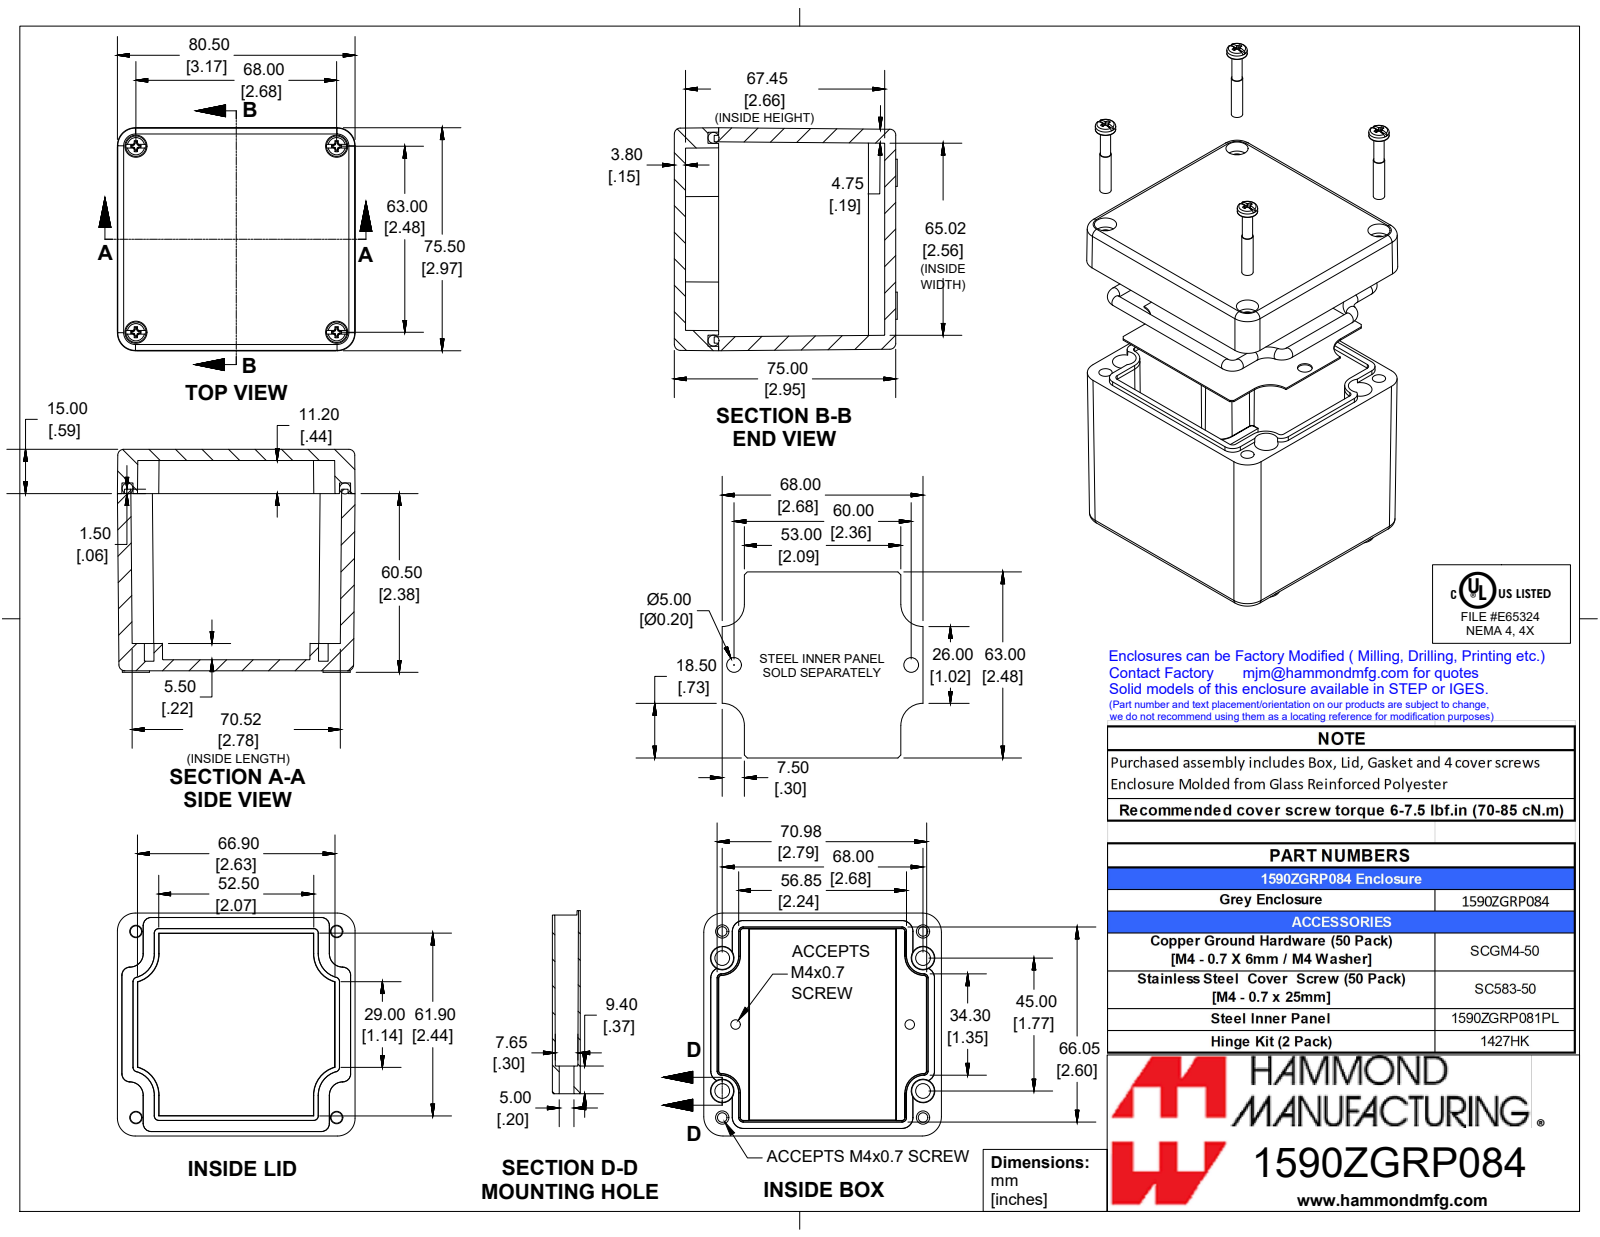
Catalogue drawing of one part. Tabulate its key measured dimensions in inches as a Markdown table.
| quantity | value |
| --- | --- |
| part name | 1590ZGRP084 |
| STEP written by | SolidWorks 2019 (CONFIG_CONTROL_DESIGN) |
| units | inches |
| bodies | 8 solids, 447 faces (233 planar, 86 cylindrical, 128 other) |
| overall size | 3.169 × 2.972 × 2.972 |
| volume | 10.01 in³ |
| surface area | 132.2 in² |
| round holes (diameter × count) | 0.128 × 6, 0.197 × 6, 0.167 × 4, 0.177 × 4, 0.295 × 4, 0.315 × 4 |
| round bosses / shafts (diameter × count) | 0.146 × 6, 0.362 × 4, 0.272 × 4, 0.152 × 4, 0.137 × 4 |
| partial cylindrical surfaces (radius × count) | 0.079 × 8, 0.004 × 6, 0.008 × 4, 0.236 × 4, 0.256 × 4, 0.295 × 4 |
| main face-to-face distances | 0.187, 2.953, 0.364, 2.589, 0.384, 2.439, 0.02, 2.569, 2.803, 2.419 |
| hole center spacings | 0.354, 0.904, 1.253, 2.126, 2.652, 2.677, 2.7, 2.791 |
